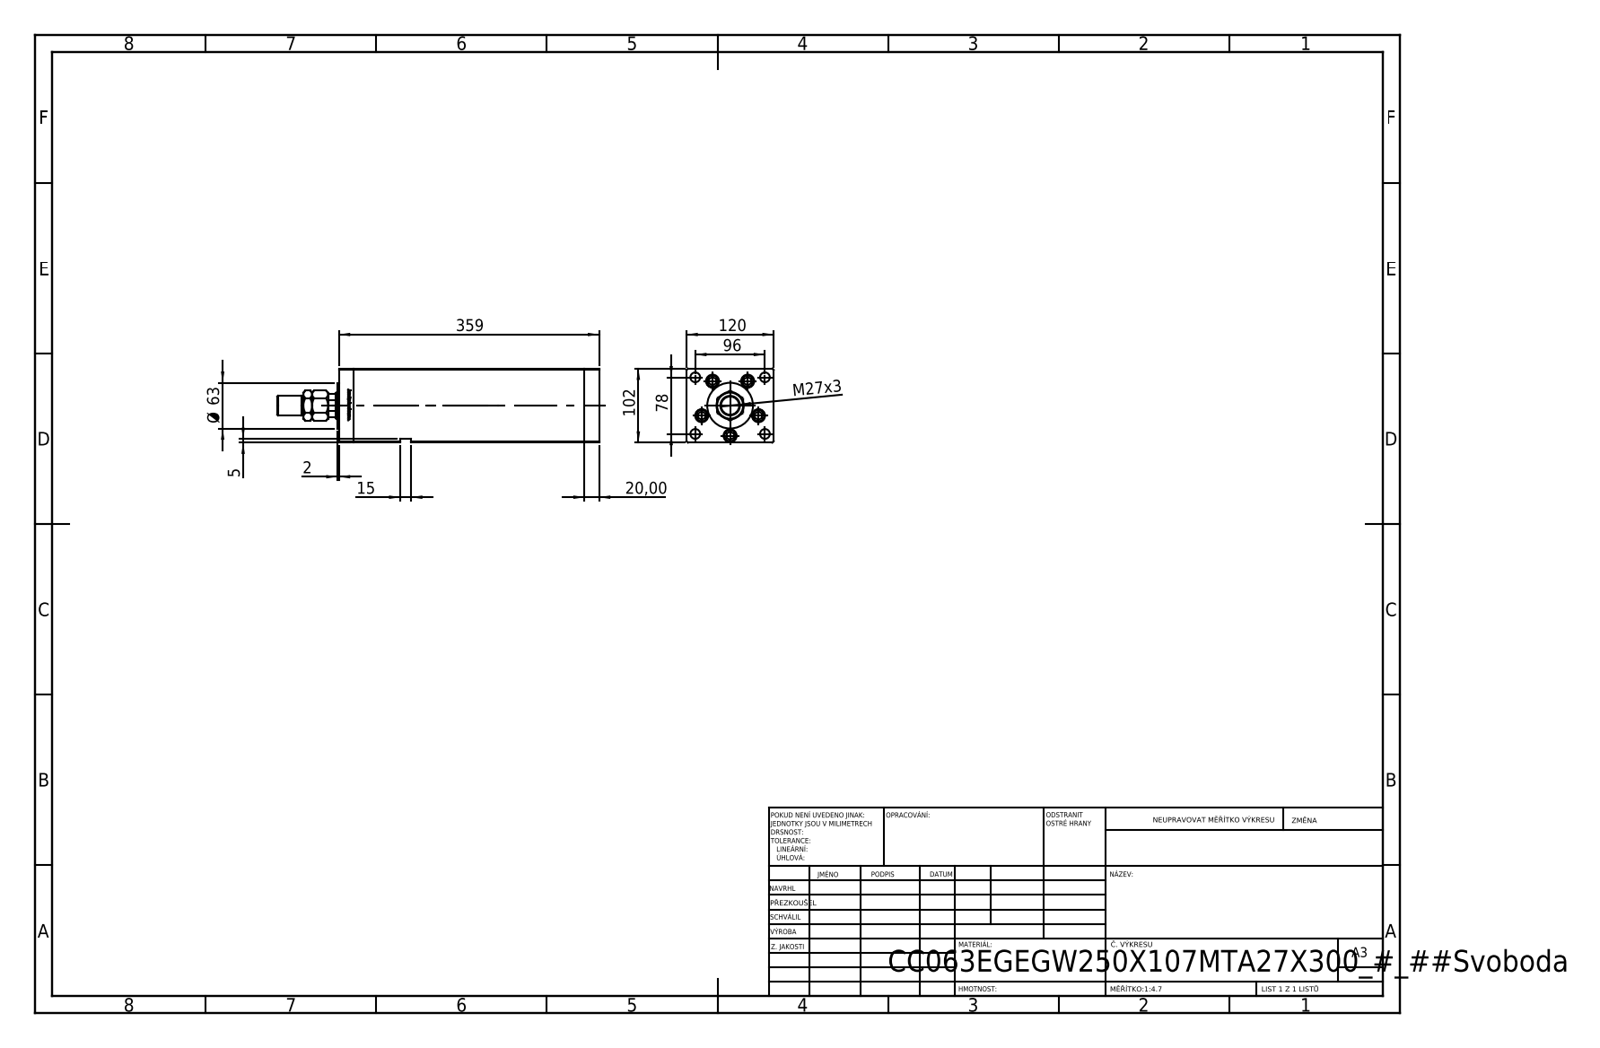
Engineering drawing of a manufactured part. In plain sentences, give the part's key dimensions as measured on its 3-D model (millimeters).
The part is named "V220C_FRONT_E; MTA; V220C_VC_E; V220C_E MIDDLE (+2 more)". Its 3-D file was written by "SolidWorks 2019 (CONFIG_CONTROL_DESIGN)". It is 15 solids with 1263 faces: 490 planar, 169 cylindrical and 604 other. Overall it measures 443.5 by 120 by 102 millimeters. Its volume is 3 720 000 cubic millimeters and its surface area 415 429 square millimeters. Round holes: 9 of diameter 13.5, 5 of diameter 18, 4 of diameter 12.5, 4 of diameter 18.5, 2 of diameter 2, 2 of diameter 13.16, 1 of diameter 25.5, 1 of diameter 36, 1 of diameter 37.5. Round bosses or shafts: 5 of diameter 17, 5 of diameter 8, 1 of diameter 63, 1 of diameter 27, 1 of diameter 25. Partial cylindrical surfaces (rounded edges, fillets, slot ends): 2 of radius 0.93, 1 of radius 17.5. The main face-to-face distances are 120, 102, 20, 318.5, 338.5, 34.25, 358.5, 14.25, 304.25, 324.25. The hole center spacings are 41.5, 61.85, 24.39, 26.69, 47.92, 48.07, 49.84, 53.57.
